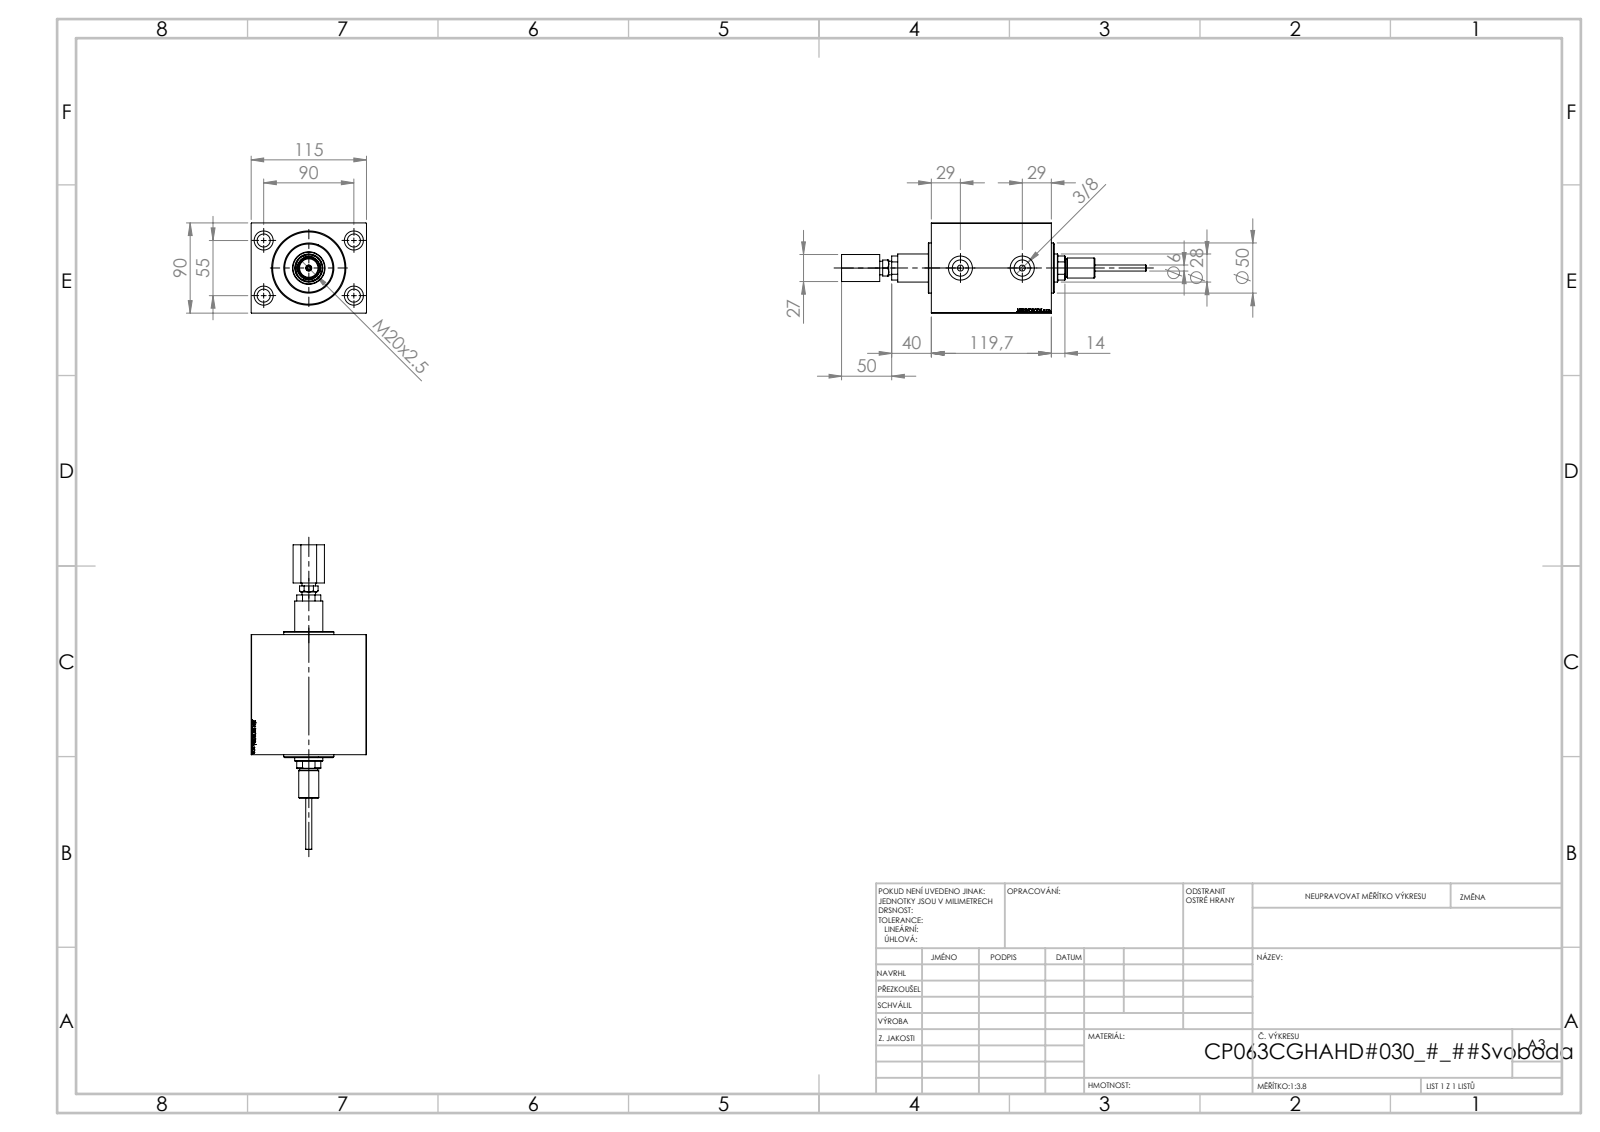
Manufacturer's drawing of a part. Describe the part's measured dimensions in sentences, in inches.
The part is named "V450DCP_B_RodCooling_ACCESSORIES; V450DCP_B_VCP; V450CP_MALE_METRIC; V450DCP_C_Body (+1 more)". Its 3-D file was written by "SolidWorks 2019 (CONFIG_CONTROL_DESIGN)". It is 5 solids with 970 faces: 446 planar, 106 cylindrical and 418 other. Overall it measures 11.957 by 4.528 by 3.543 inches. Its volume is 69.75 cubic inches and its surface area 273.5 square inches. Round holes: 4 of diameter 0.512, 4 of diameter 0.748, 3 of diameter 0.236, 2 of diameter 0.157, 2 of diameter 0.383, 2 of diameter 0.591, 2 of diameter 0.637, 2 of diameter 0.945, 1 of diameter 0.118, 1 of diameter 0.728, 1 of diameter 1.102, 1 of diameter 1.24. Round bosses or shafts: 1 of diameter 1.969, 1 of diameter 0.787, 1 of diameter 0.709, 1 of diameter 0.53. Partial cylindrical surfaces (rounded edges, fillets, slot ends): 1 of radius 0.531. The main face-to-face distances are 3.543, 4.528, 4.024, 1.181, 4.713, 0.689, 0.039, 4.673, 0.65, 1.661. The hole center spacings are 2.076, 2.165, 3.543, 4.153, 1.662, 2.429.
